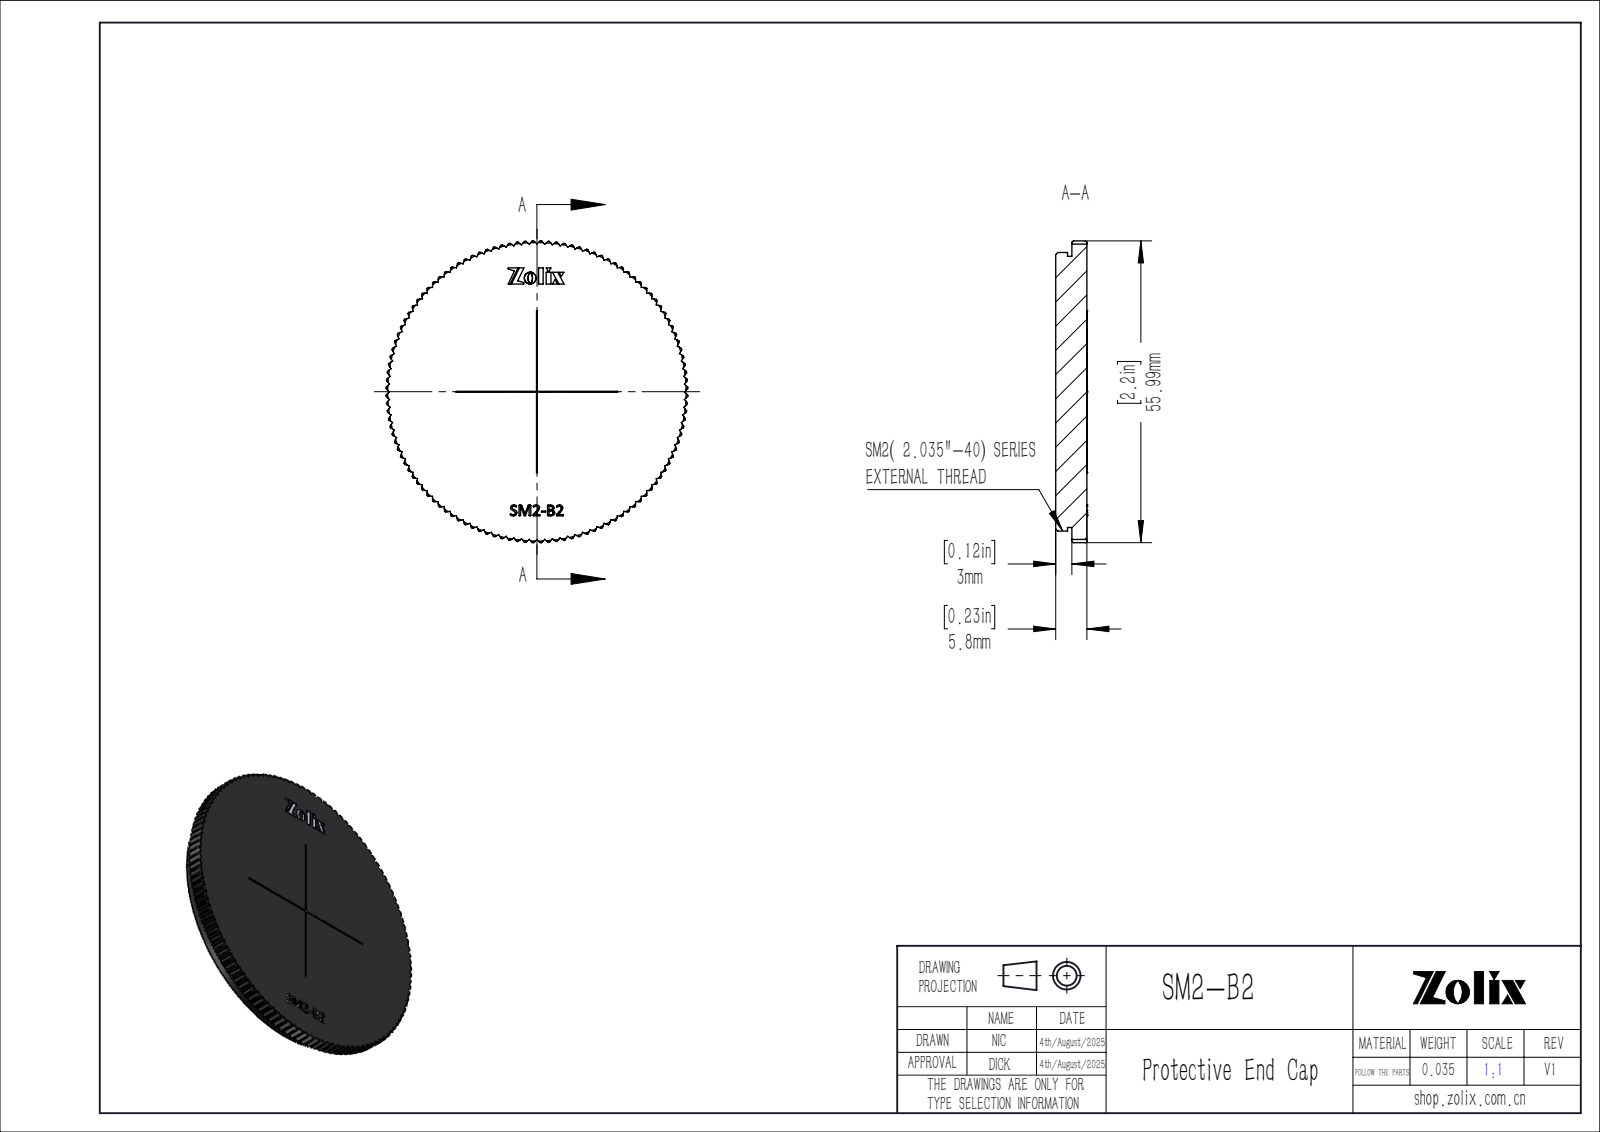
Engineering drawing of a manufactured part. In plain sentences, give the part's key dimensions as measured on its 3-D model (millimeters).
The part is named "SM2-B2". Its 3-D file was written by "SolidWorks 2020 (CONFIG_CONTROL_DESIGN)". It is 1 solid with 894 faces: 470 planar, 124 cylindrical and 300 other. Overall it measures 55.99 by 55.99 by 5.8 millimeters. Its volume is 12 965 cubic millimeters and its surface area 6 153 square millimeters. Round bosses or shafts: 1 of diameter 51.69, 1 of diameter 50.3. Partial cylindrical surfaces (rounded edges, fillets, slot ends): 1 of radius 28. The main face-to-face distances are 5.8, 3, 2.8, 38.74, 3.6, 0.8, 2.2, 38.76, 38.75, 2.78.
